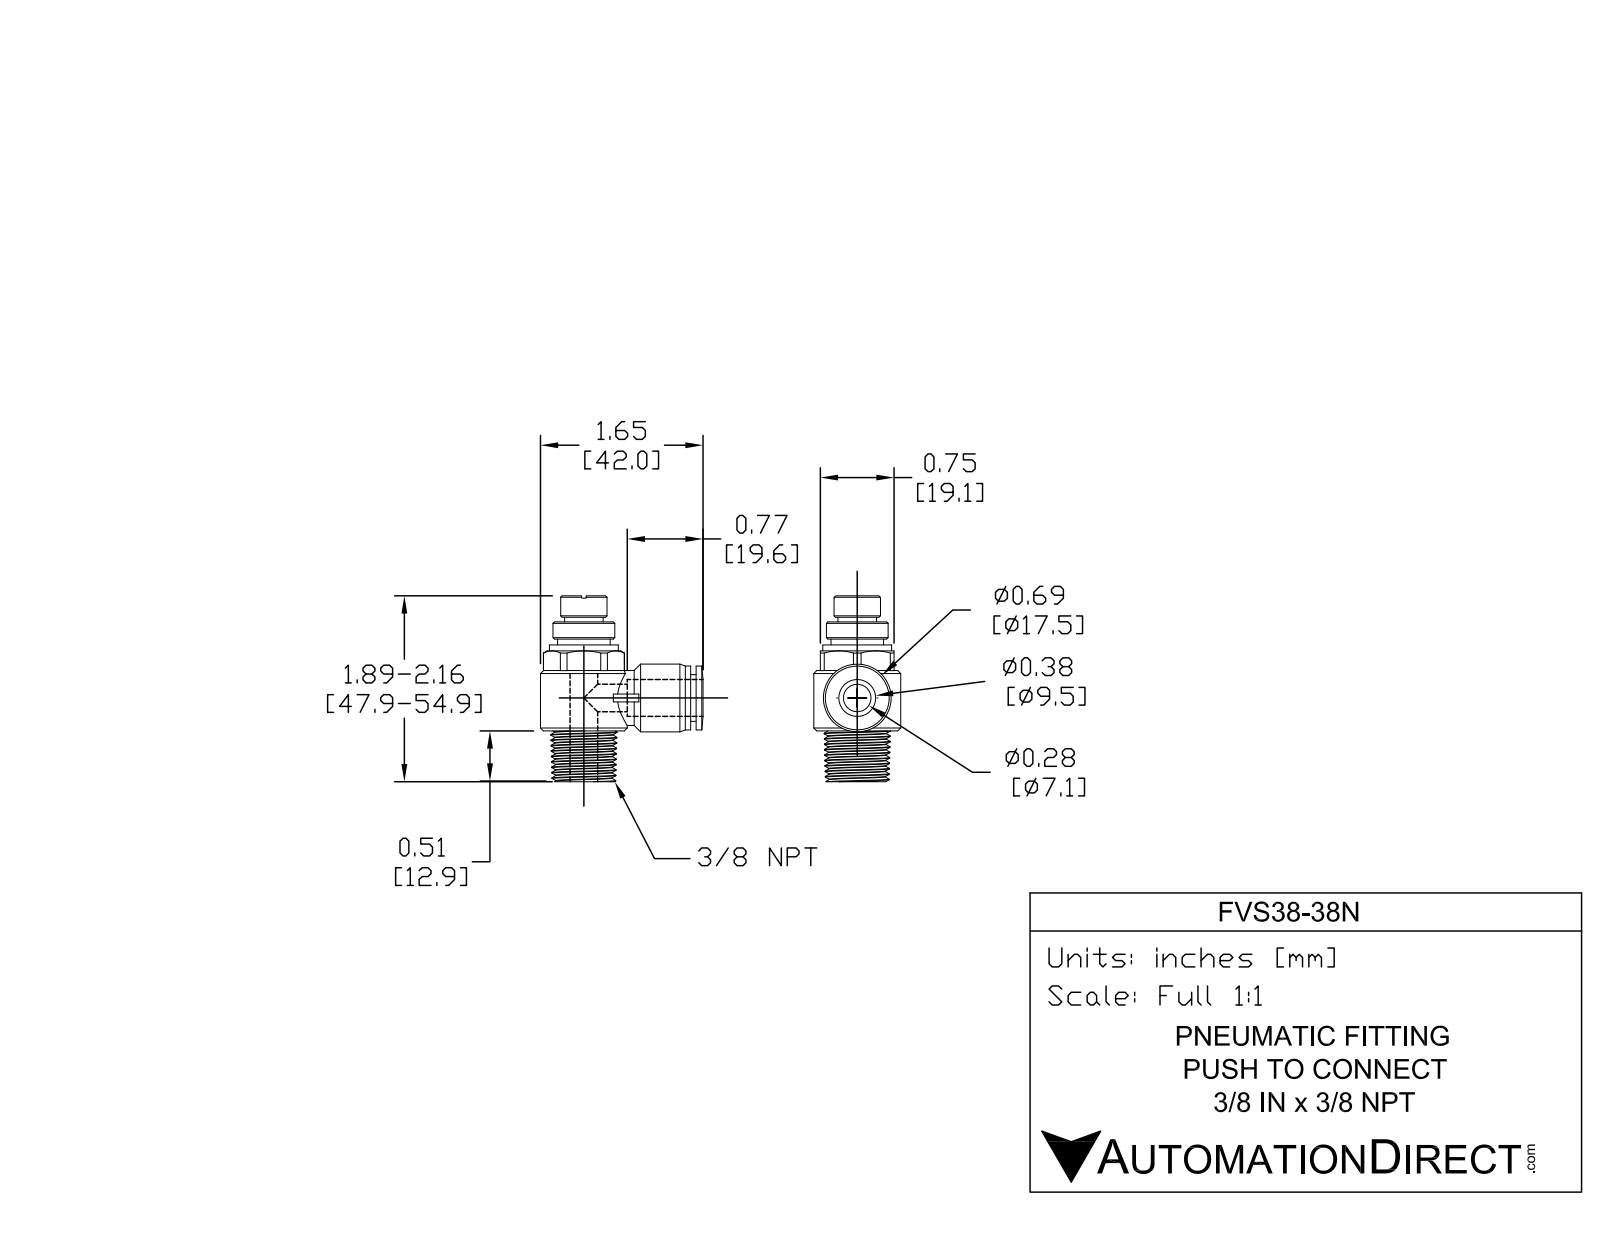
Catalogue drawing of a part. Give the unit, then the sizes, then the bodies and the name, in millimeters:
Units: millimetres
Overall size (bounding box): 54.9 × 42 × 22.5
Round holes (diameter × count): ⌀6 ×2, ⌀9.8 ×1
Round bosses / shafts (diameter × count): ⌀22.5 ×1, ⌀19 ×1, ⌀17.5 ×1, ⌀17.2 ×1, ⌀17 ×1, ⌀16.8 ×1, ⌀15 ×1, ⌀14 ×1
Partial cylindrical surfaces — rounded edges, fillets, slot ends (radius × count): R6 ×1, R8 ×1, R10.5 ×1
Main face-to-face distances: 19, 1.2, 5.8, 20.6, 26.4, 10.9, 14.1, 34.7, 40.5, 54.9
Volume: 14 700 mm³ · Surface area: 6 437 mm²
Bodies: 1 solid, 558 faces (252 planar, 143 cylindrical, 163 other)
Part name (STEP PRODUCT): FVS38-38N
STEP written by: SolidWorks 2015 (AUTOMOTIVE_DESIGN)
